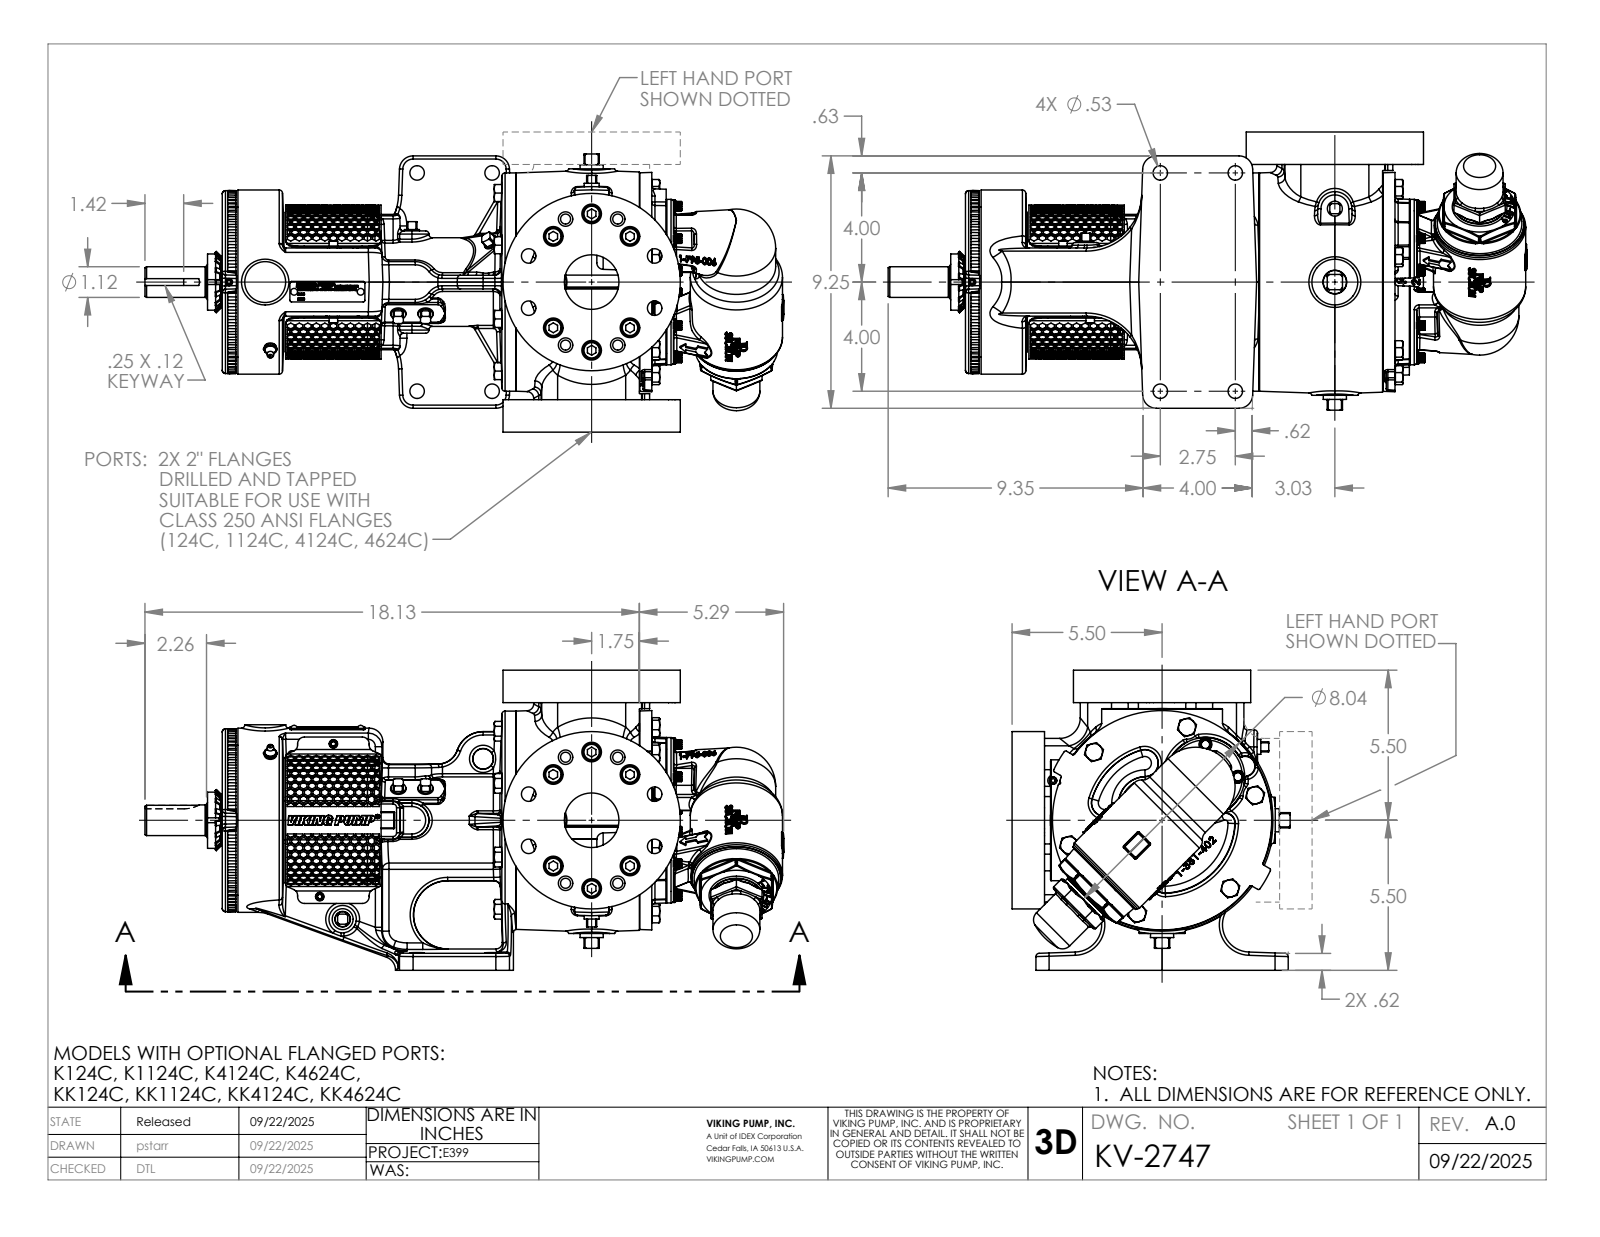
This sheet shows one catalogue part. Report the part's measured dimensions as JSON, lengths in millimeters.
{"part_name": "KV-2747", "step_written_by": "SolidWorks 2024 (AUTOMOTIVE_DESIGN)", "units": "millimeters", "bodies": {"solids": 1, "faces": 5879, "planar": 2073, "cylindrical": 817, "other": 2989}, "overall_size": [594.8, 279.4, 258.95], "volume_mm3": 10180000, "surface_area_mm2": 762326, "round_holes": [[13.49, 16], [18.26, 12], [6.35, 9], [9.35, 8], [19.81, 8], [5.02, 6], [13.49, 4], [4.04, 2], [7.94, 2], [50.8, 2], [6.53, 1], [11.51, 1]], "round_bosses_or_shafts": [[15.88, 23], [11.91, 8], [73.15, 3], [15.87, 3], [7.92, 3], [4.83, 3], [165.1, 2], [82.55, 2]], "partial_cylinders_radius": [[3.05, 78], [0.76, 37], [6.1, 18], [25.4, 18], [3.05, 16], [6.35, 10], [12.7, 10], [2.29, 8]], "face_to_face_distances": [279.4, 30.23, 12.7, 400.03, 135.23, 264.8, 14.58, 120.65, 385.45, 249.17], "hole_center_spacings": [63.5, 76.2, 26.16, 48.6, 24.78, 29.33, 34.96, 55.56]}
